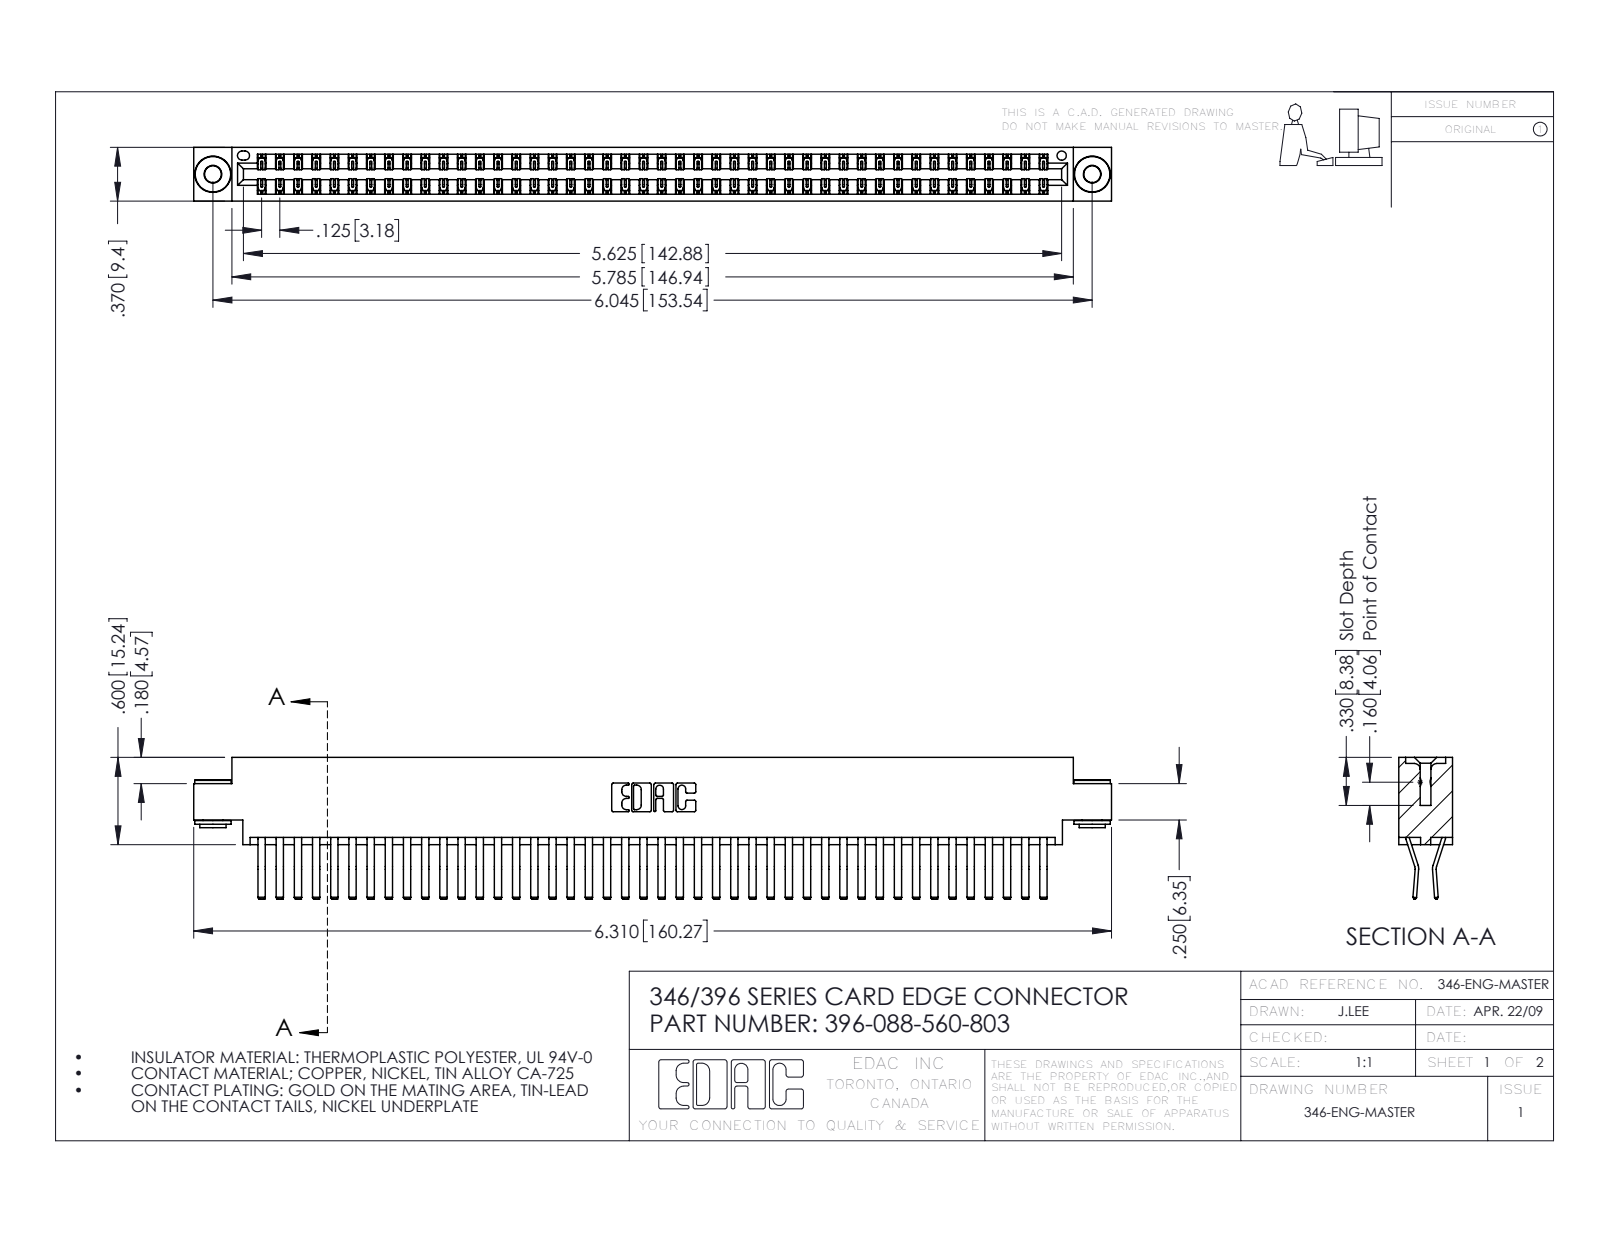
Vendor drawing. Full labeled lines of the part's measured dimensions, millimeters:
Part name (STEP PRODUCT): 396-088-560-803; 346 Part_0.170 Offset - 0.156 Dia-TH; 345-292-001_560 Tail; 345-250-002_345-250-002-102
STEP written by: SolidWorks 2016 (CONFIG_CONTROL_DESIGN)
Units: millimetres
Bodies: 91 solids, 4916 faces (3170 planar, 1738 cylindrical, 8 other)
Overall size (bounding box): 160.3 × 24.8 × 9.4
Volume: 16 100 mm³ · Surface area: 24 080 mm²
Round holes (diameter × count): ⌀2.9 ×2, ⌀4 ×2, ⌀1.6 ×1
Round bosses / shafts (diameter × count): ⌀6.4 ×2, ⌀4.6 ×2, ⌀3.5 ×2
Partial cylindrical surfaces — rounded edges, fillets, slot ends (radius × count): R0.2 ×132, R0.3 ×22, R0.2 ×6, R0.8 ×6, R0.7 ×3, R0.3 ×2, R0.4 ×2, R0.6 ×2
Main face-to-face distances: 1.2, 8.2, 9.4, 0.6, 6.4, 7, 1.8, 7.6, 3.8, 5.6
Hole centre spacings: 6.2, 148.2, 153.5
